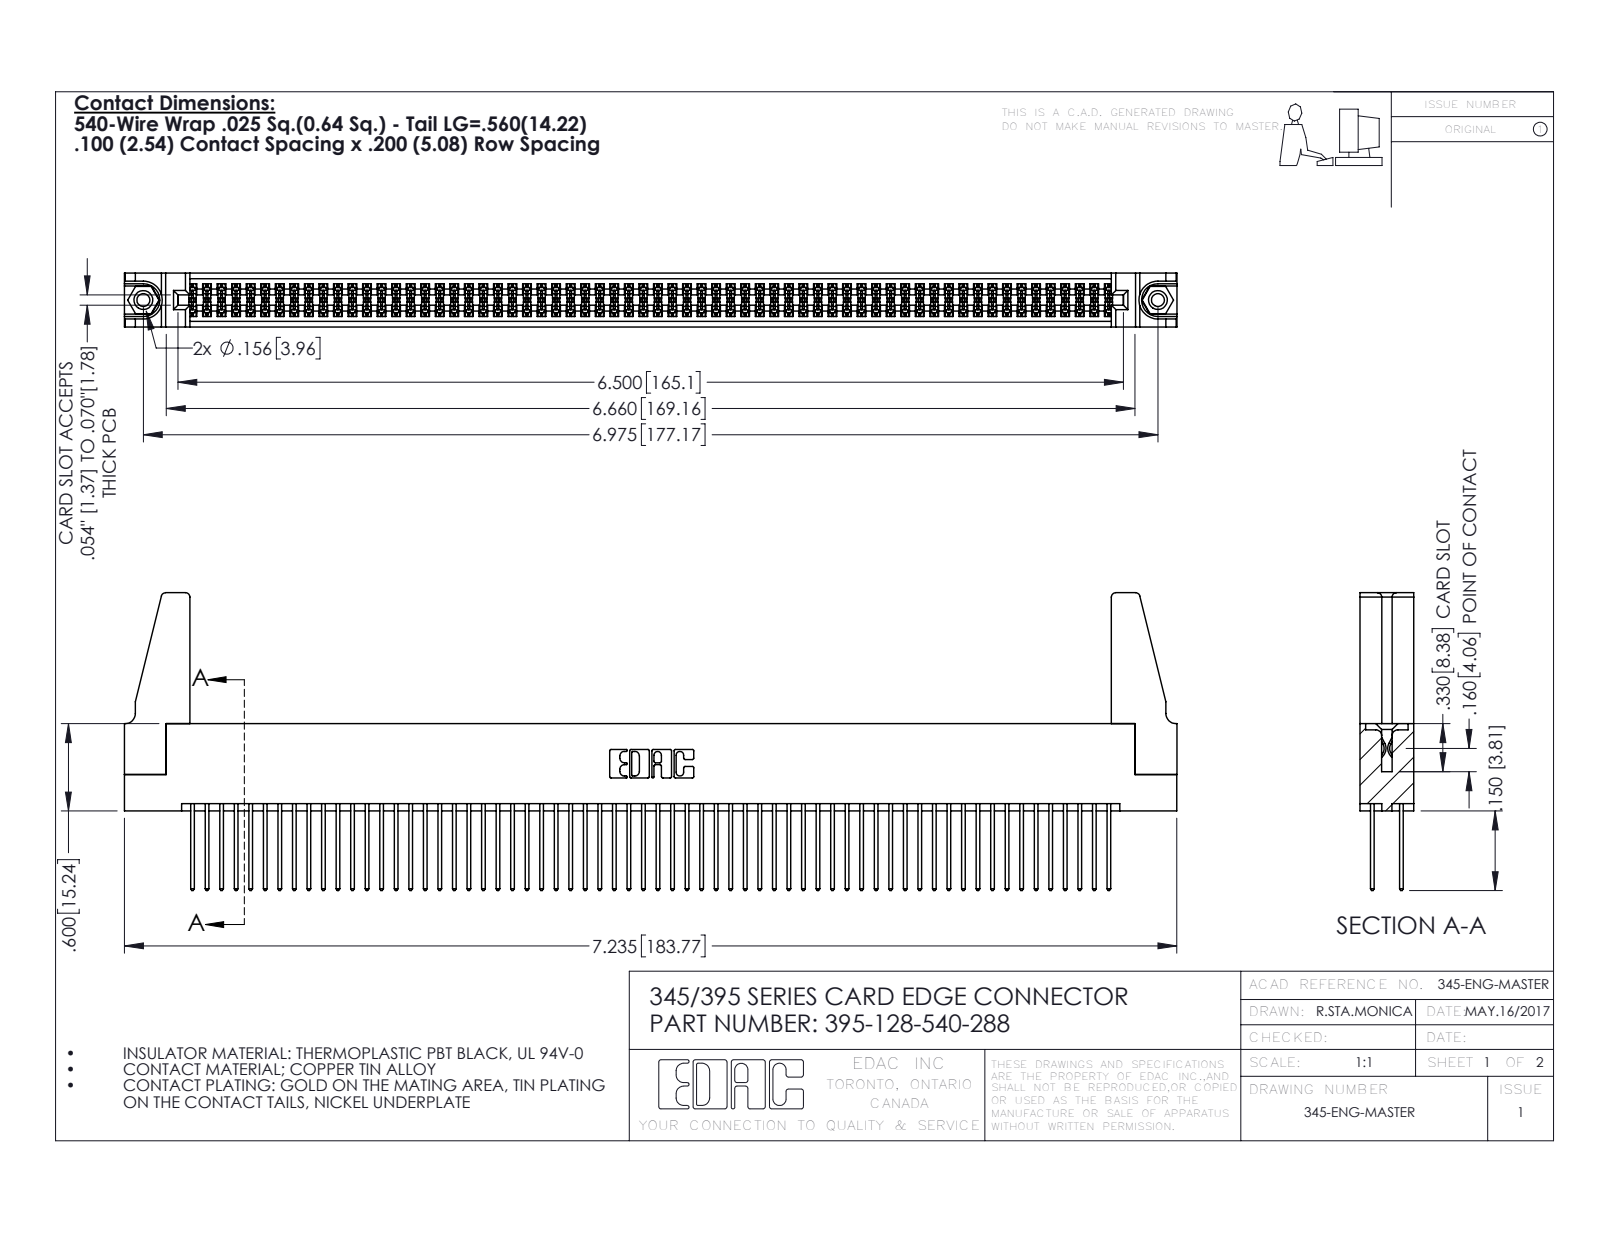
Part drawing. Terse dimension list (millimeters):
name: 345-250-001_345-250-001-102; 395-128-540-288; 345 Part_Flush Mounting Lugs - 0.156 Dia-TH; 345-292-001_345-293-140 (+1 more)
written by: SolidWorks 2016 (CONFIG_CONTROL_DESIGN)
unit: mm
bodies: 133 solids, 6650 faces (4376 planar, 2258 cylindrical, 16 other)
size: 183.8 × 52 × 9.4
volume: 21 790 mm³; area: 33 210 mm²
holes: 2× ⌀2.3, 2× ⌀3.2, 2× ⌀4, 1× ⌀1.6
bosses: 2× ⌀3.9
rounds: 192× R0.2, 128× R0.3, 22× R0.3, 8× R0.8, 6× R0.2, 6× R0.8, 3× R0.7, 2× R0.4
face distances: 1.8, 7.6, 5.1, 2.5, 6.9, 0.6, 9.4, 5.7, 4.4, 3.8
hole spacings: 6.9, 171.2, 177.2
